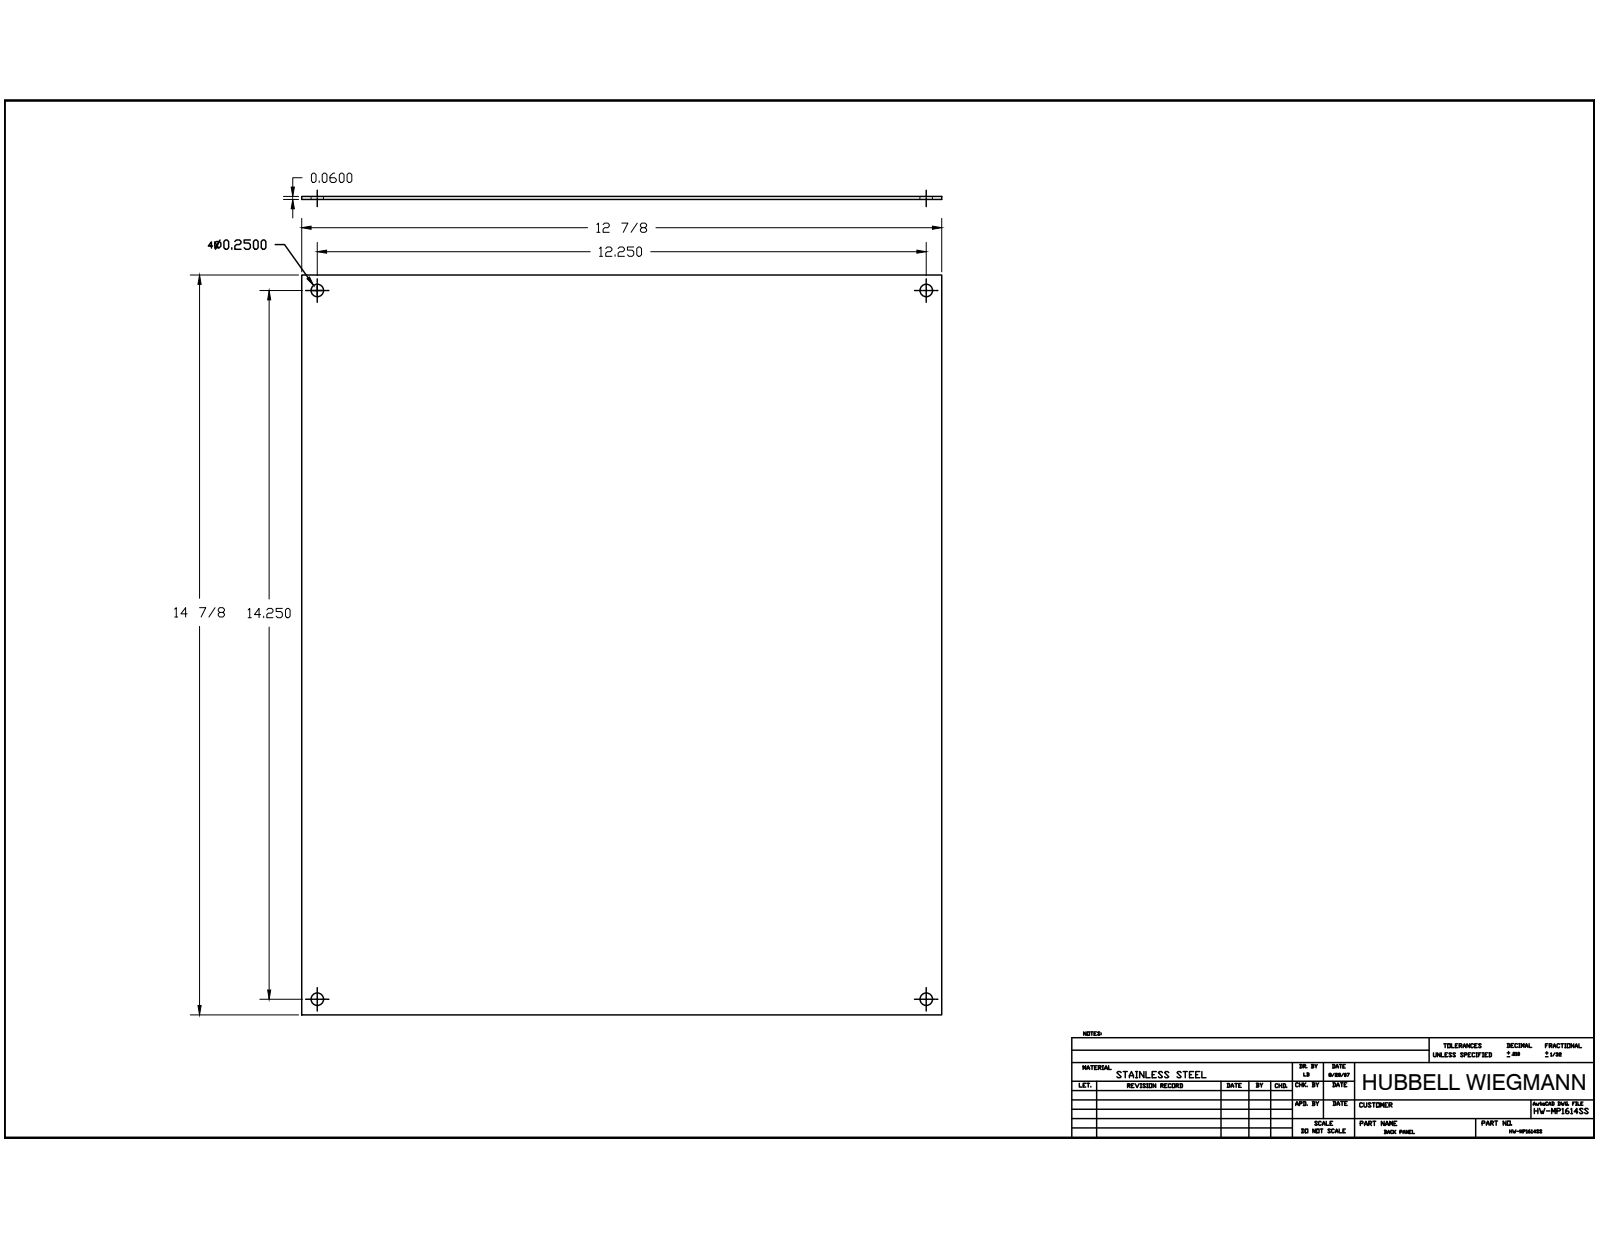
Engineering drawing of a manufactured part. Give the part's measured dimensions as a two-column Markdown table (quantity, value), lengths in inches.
| quantity | value |
| --- | --- |
| part name | BP1614SS_STP |
| STEP written by | Autodesk Inventor 2014 (AUTOMOTIVE_DESIGN) |
| units | inches |
| bodies | 1 solid, 10 faces (6 planar, 4 cylindrical, 0 other) |
| overall size | 14.875 × 12.875 × 0.06 |
| volume | 11.48 in³ |
| surface area | 386.2 in² |
| round holes (diameter × count) | 0.25 × 4 |
| main face-to-face distances | 0.06, 12.875, 14.875 |
| hole center spacings | 12.25, 14.25, 18.791 |
